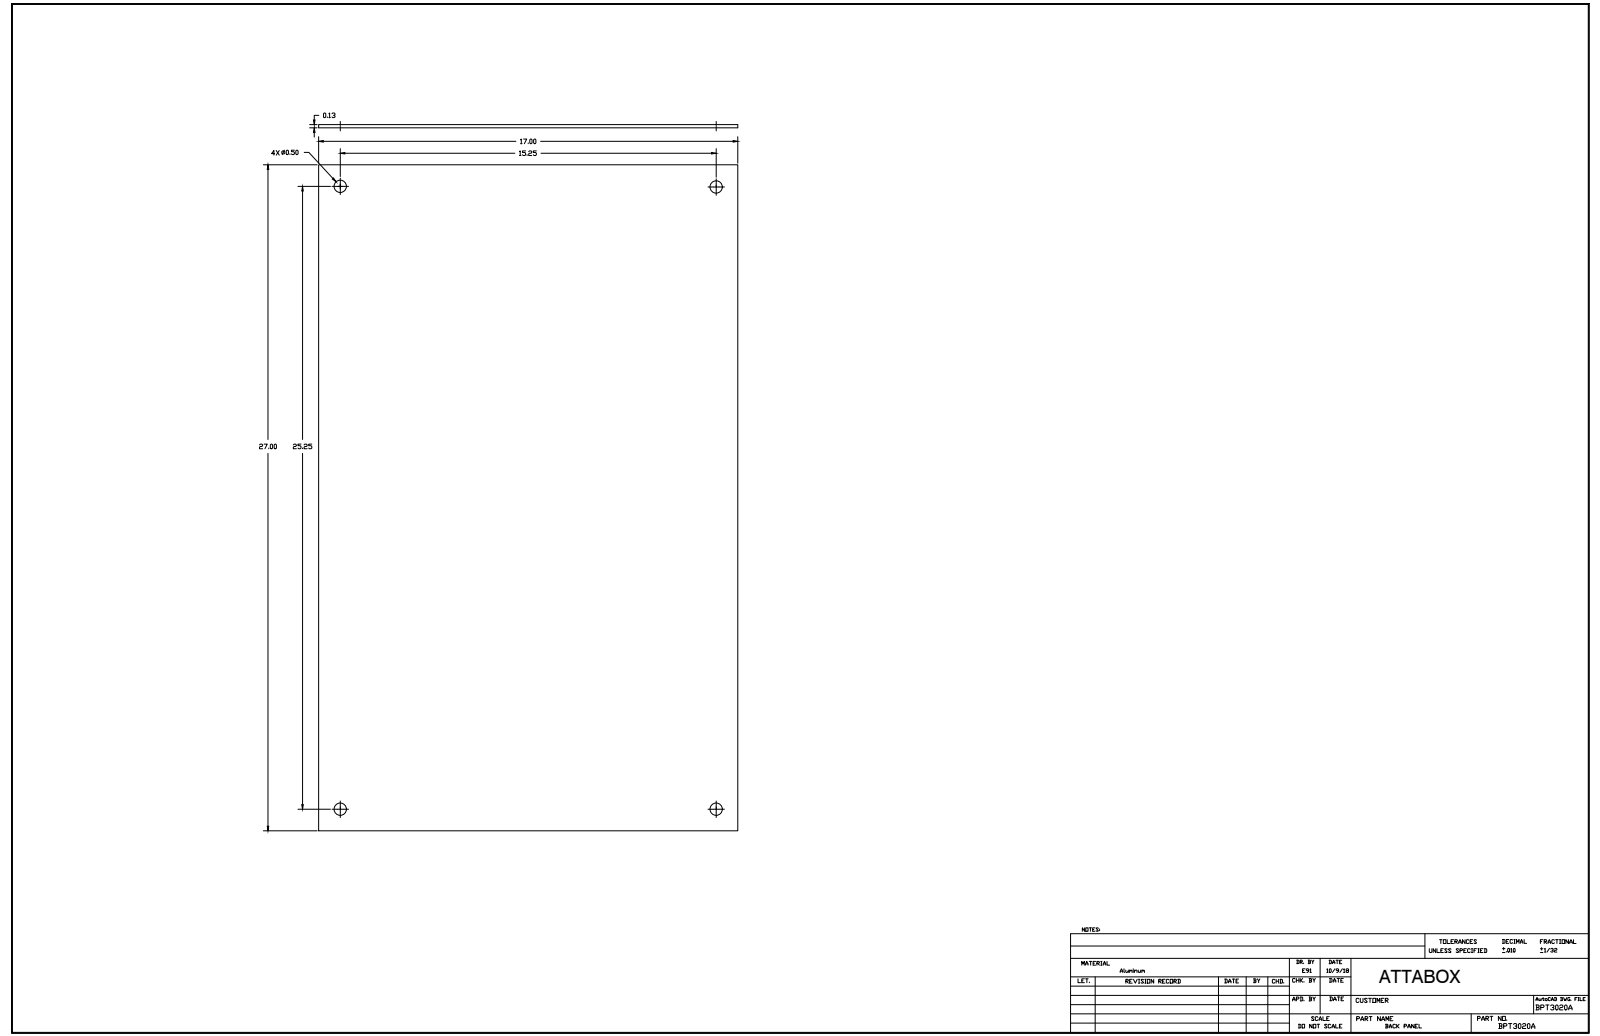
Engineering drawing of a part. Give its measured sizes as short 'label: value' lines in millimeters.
name: BP3020AL_STP
written by: Autodesk Inventor 2014 (AUTOMOTIVE_DESIGN)
unit: mm
bodies: 1 solid, 10 faces (6 planar, 4 cylindrical, 0 other)
size: 685.8 × 431.8 × 3.3
volume: 976 143 mm³; area: 599 151 mm²
holes: 4× ⌀12.7
face distances: 3.3, 431.8, 685.8
hole spacings: 387.34, 641.34, 749.23
